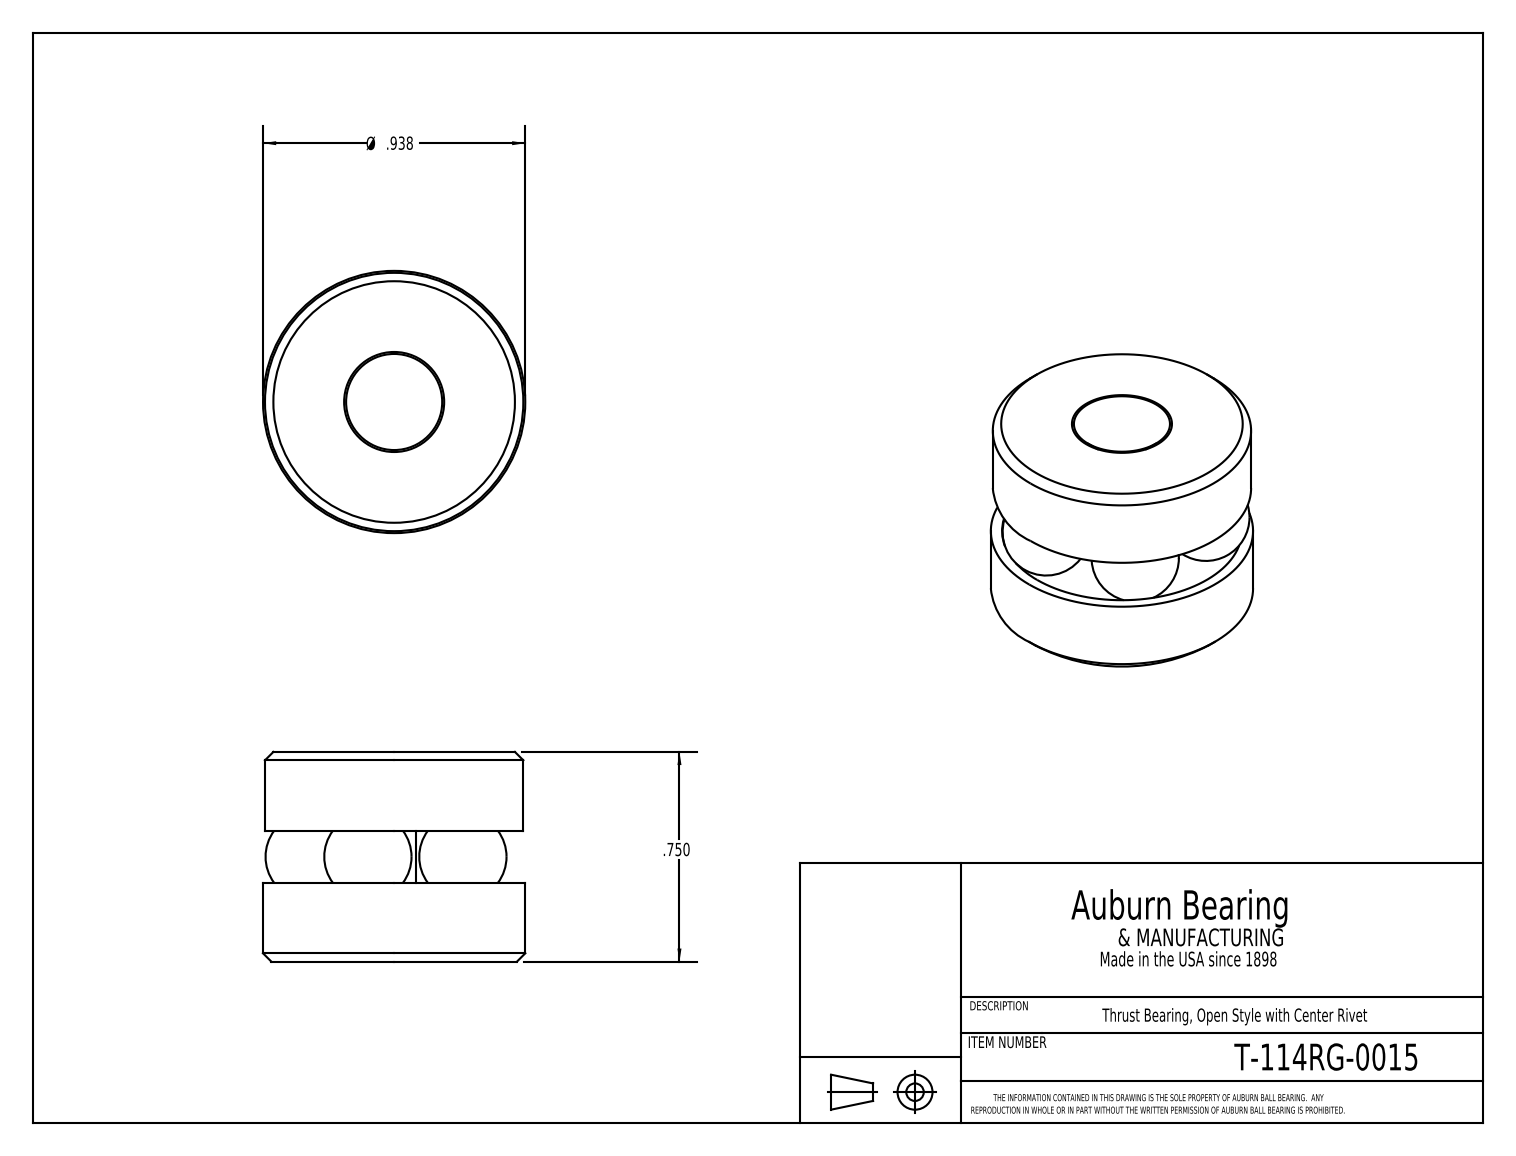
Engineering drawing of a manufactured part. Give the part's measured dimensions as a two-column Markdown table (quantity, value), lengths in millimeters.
| quantity | value |
| --- | --- |
| part name | T-114RG_T-114RG-0015 |
| STEP written by | SolidWorks 2016 (CONFIG_CONTROL_DESIGN) |
| units | millimeters |
| bodies | 8 solids, 26 faces (8 planar, 5 cylindrical, 13 other) |
| overall size | 23.8 × 23.8 × 19.1 |
| volume | 6 880 mm³ |
| surface area | 4 375 mm² |
| round holes (diameter × count) | 4.2 × 1 |
| round bosses / shafts (diameter × count) | 23.8 × 1, 23.4 × 1, 4 × 1 |
| main face-to-face distances | 19.1, 7.1, 11.9, 4.7 |
